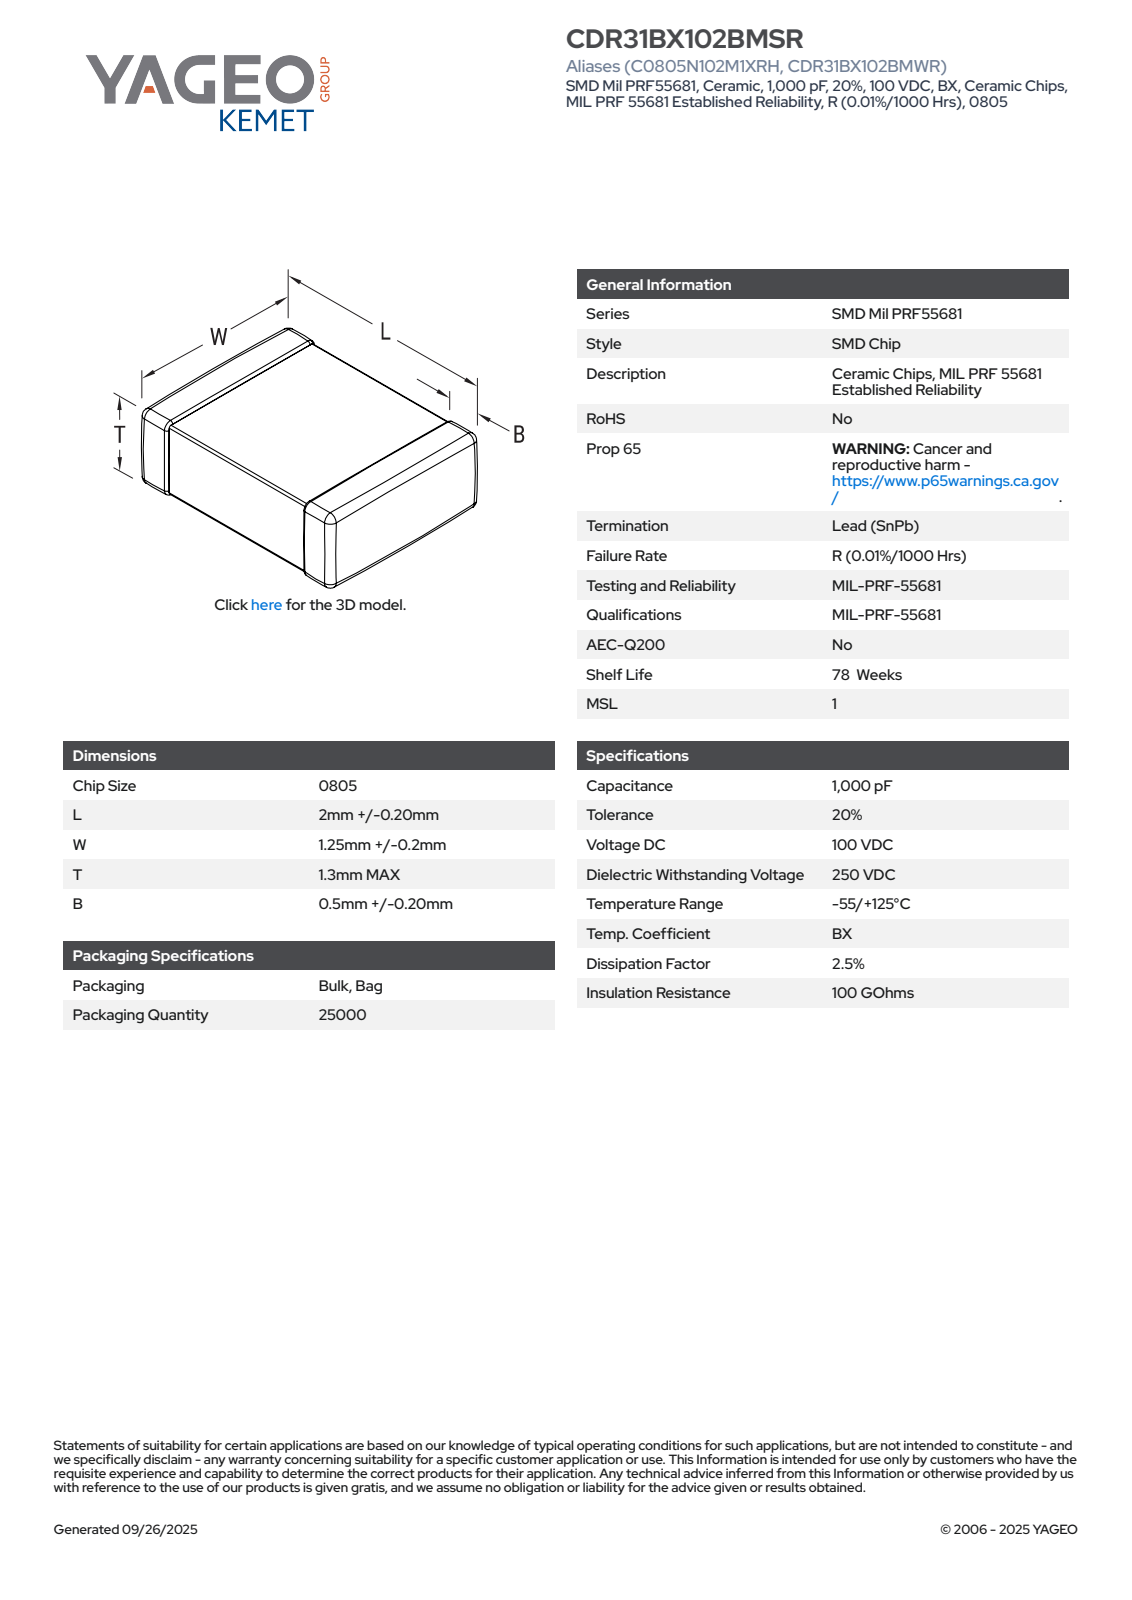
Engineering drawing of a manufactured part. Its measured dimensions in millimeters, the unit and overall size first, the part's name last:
Units: millimetres
Overall size (bounding box): 2.2 × 1.45 × 1.3
Main face-to-face distances: 1.27, 1.42, 1.3, 2.2, 1.45, 1.24, 1.39, 0.68, 0.65, 0.77
Volume: 4 mm³ · Surface area: 16 mm²
Bodies: 4 solids, 125 faces (71 planar, 38 cylindrical, 16 other)
Part name (STEP PRODUCT): CCS_STDNOS_0805_L2.2W1.45T1.3B0.7
STEP written by: SolidWorks 2021 (AUTOMOTIVE_DESIGN)
